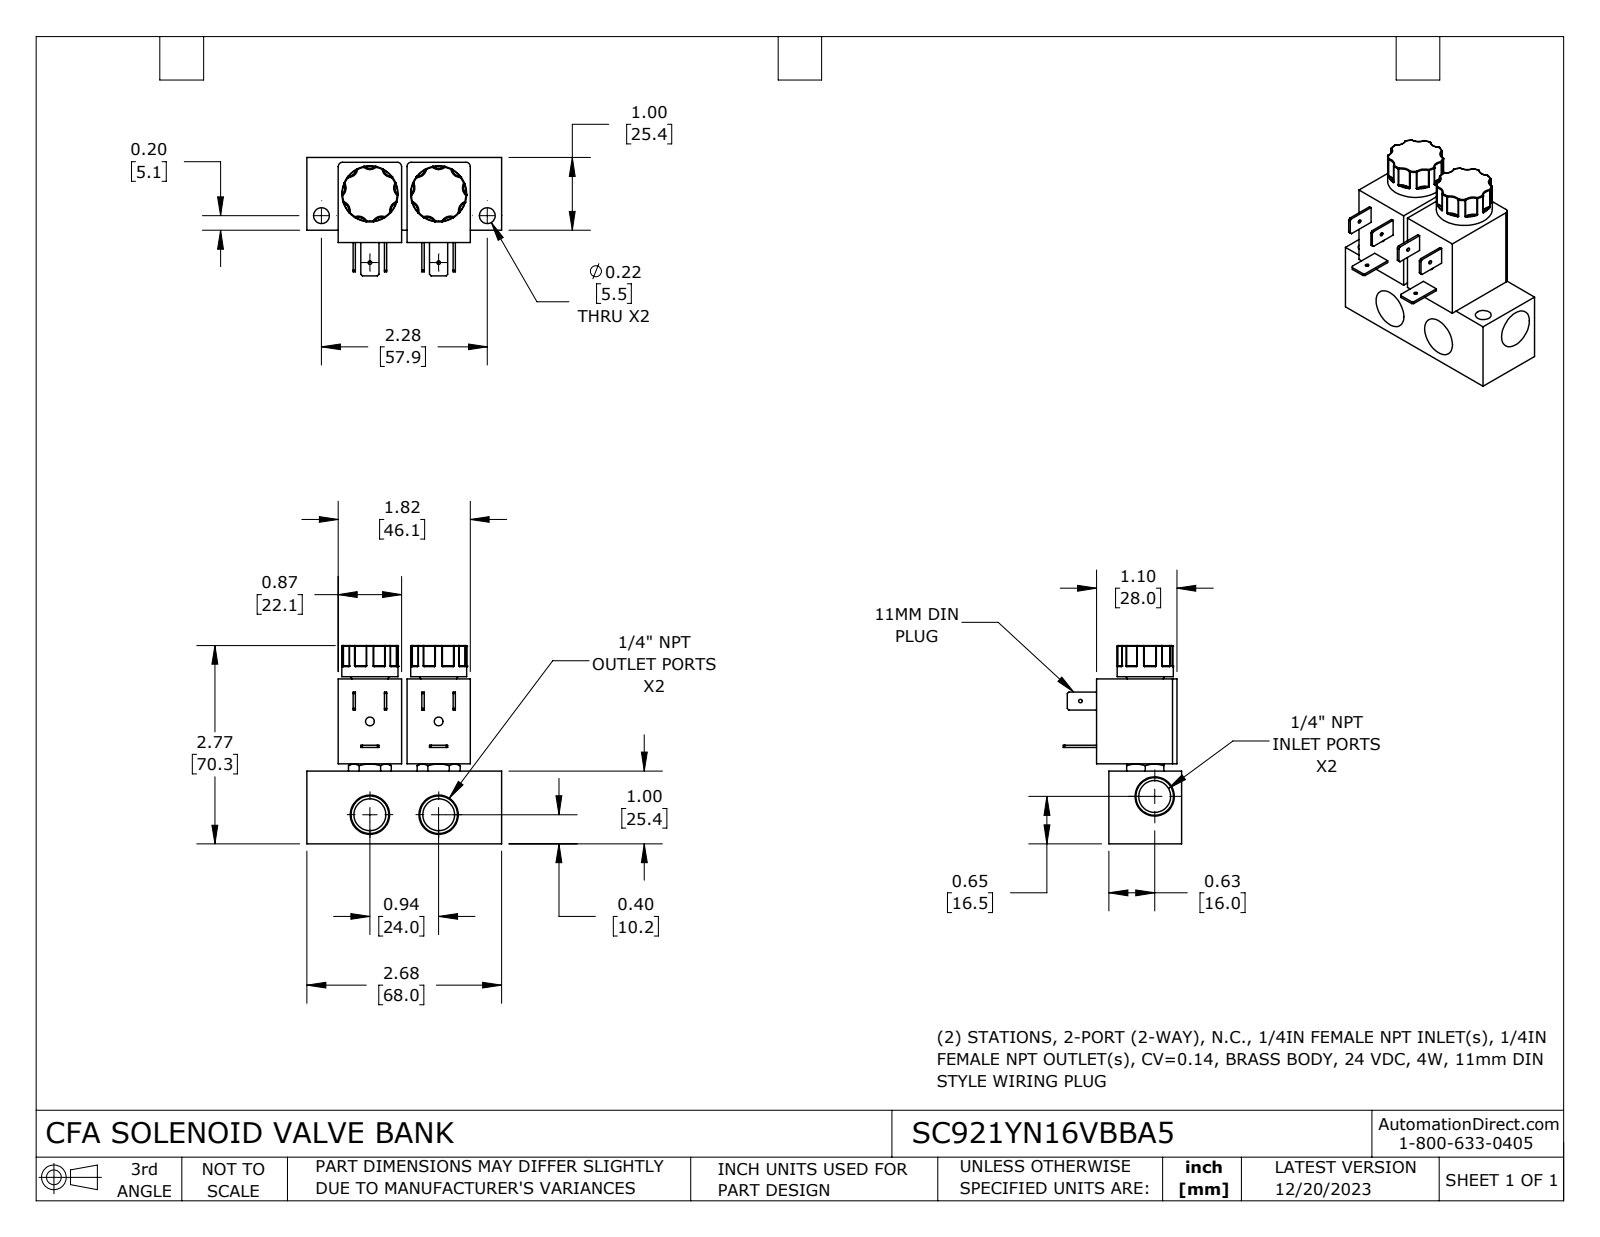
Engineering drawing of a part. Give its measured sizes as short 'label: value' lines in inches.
name: SC921YN16VBBA5
written by: SolidWorks 2023 (CONFIG_CONTROL_DESIGN)
unit: in
bodies: 1 solid, 446 faces (100 planar, 96 cylindrical, 250 other)
size: 2.725 × 2.677 × 1.627
volume: 4.833 in³; area: 34.57 in²
holes: 3× ⌀0.05, 3× ⌀0.438, 2× ⌀0.12, 2× ⌀0.217
bosses: 2× ⌀0.77
rounds: 36× R0.01, 18× R0.133, 4× R0.06
face distances: 1, 0.945, 0.87, 1.169, 0.169, 0.065, 0.935, 1.104, 0.431, 1.301
hole spacings: 0.945, 1.282, 1.593, 0.928, 0.93, 1.662, 1.735, 1.738
